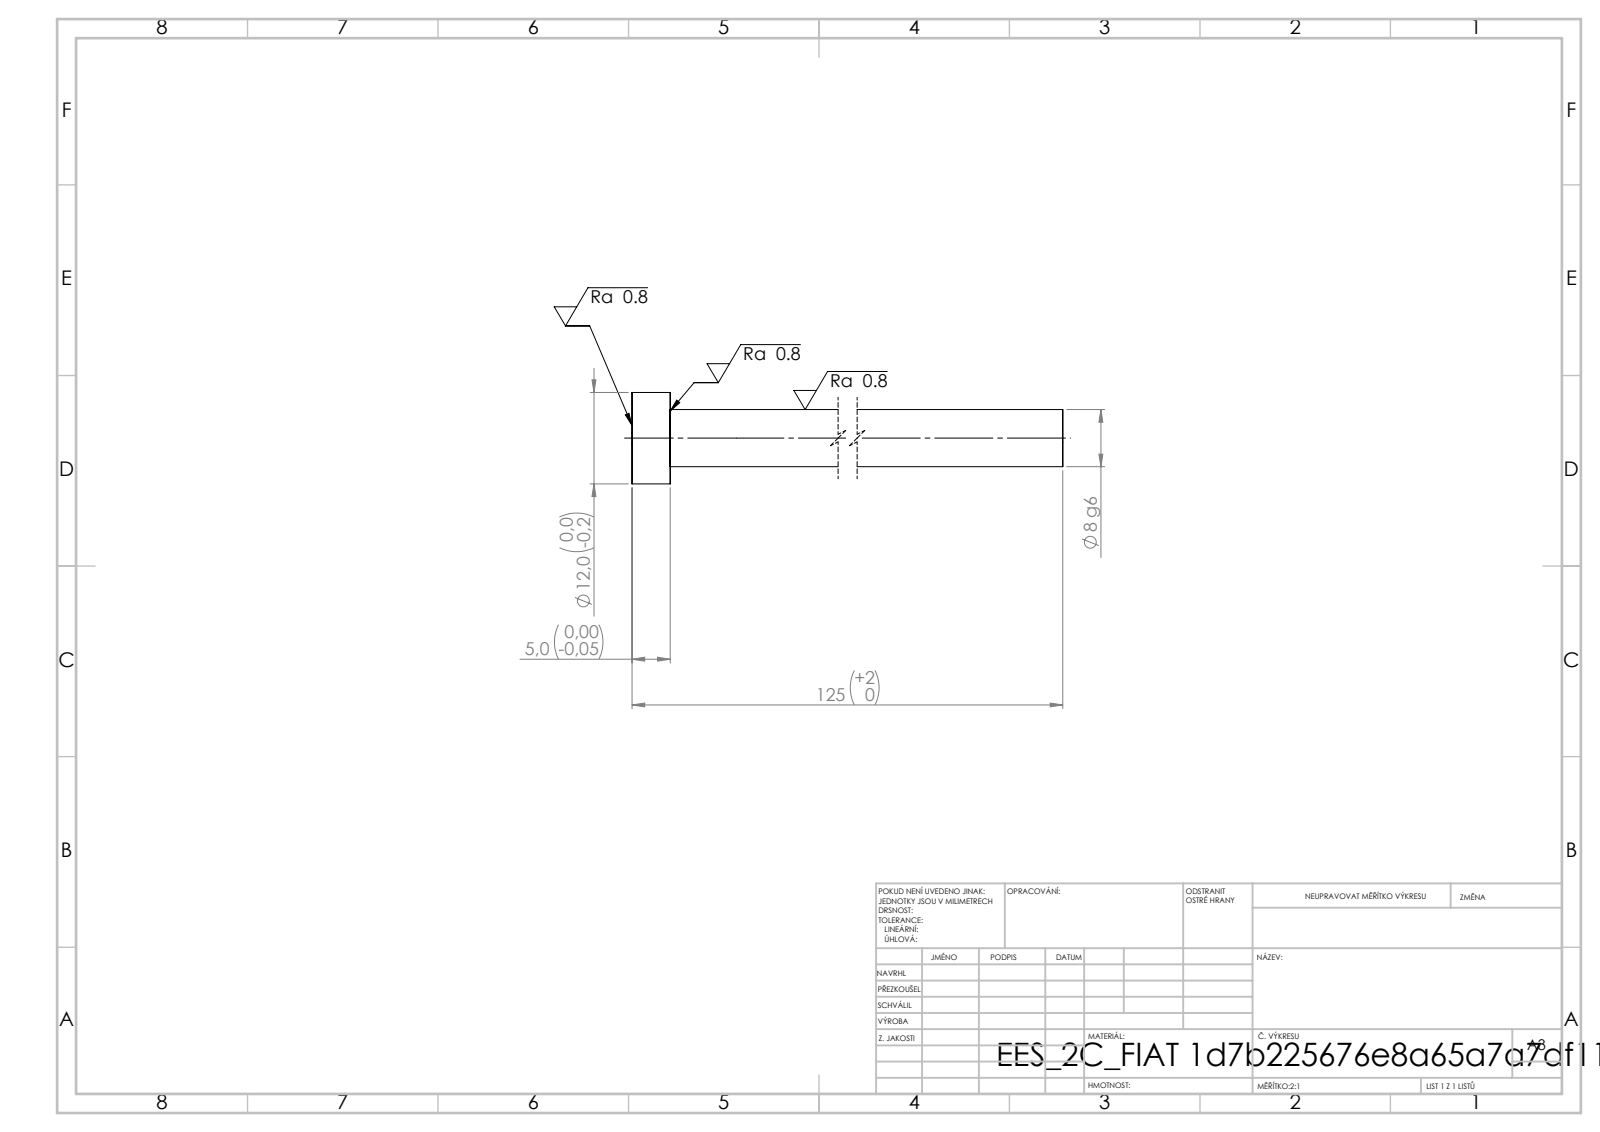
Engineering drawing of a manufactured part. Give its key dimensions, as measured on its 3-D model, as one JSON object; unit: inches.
{"step_written_by": "SolidWorks 2019 (CONFIG_CONTROL_DESIGN)", "units": "inches", "bodies": {"solids": 1, "faces": 7, "planar": 3, "cylindrical": 4, "other": 0}, "overall_size": [4.921, 0.472, 0.472], "volume_in3": 0.358, "surface_area_in2": 5.025, "round_bosses_or_shafts": [[0.472, 1], [0.295, 1]], "face_to_face_distances": [0.197, 4.921, 4.724]}
